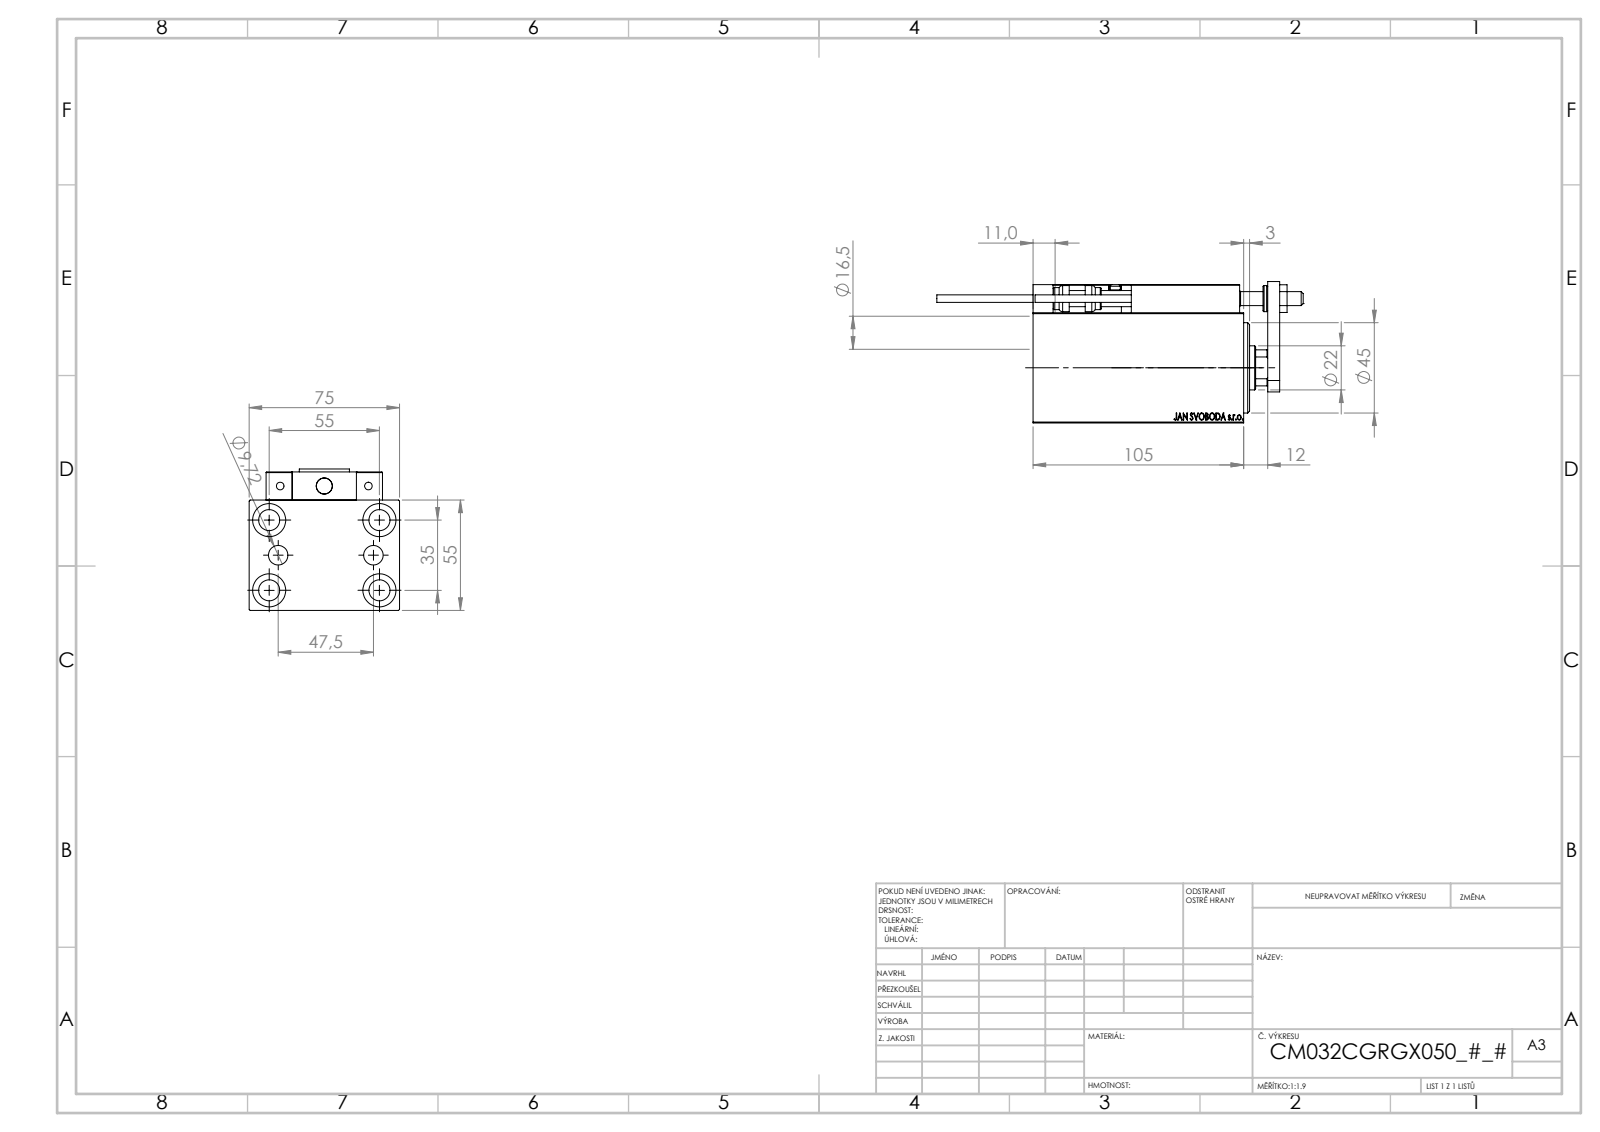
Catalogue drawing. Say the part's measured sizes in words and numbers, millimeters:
The part is named "V450CM_VC_B; MAGNET; V450CM_C_Body; V450CM_C_VCP (+7 more)". Its 3-D file was written by "SolidWorks 2019 (CONFIG_CONTROL_DESIGN)". It is 23 solids with 1278 faces: 560 planar, 184 cylindrical and 534 other. Overall it measures 182.7 by 75 by 70.5 millimeters. Its volume is 415 378 cubic millimeters and its surface area 105 587 square millimeters. Round holes: 6 of diameter 4, 5 of diameter 8, 5 of diameter 10.5, 5 of diameter 16.5, 4 of diameter 3.2, 2 of diameter 5, 2 of diameter 9.72, 1 of diameter 7, 1 of diameter 22, 1 of diameter 25.5, 1 of diameter 32, 1 of diameter 34. Round bosses or shafts: 2 of diameter 5, 2 of diameter 3.8, 1 of diameter 13, 1 of diameter 11. Partial cylindrical surfaces (rounded edges, fillets, slot ends): 30 of radius 0.3, 2 of radius 3, 1 of radius 10.5. The main face-to-face distances are 55, 75, 14, 10, 69, 5, 12, 25, 18, 3. The hole center spacings are 17.9, 32.6, 54.16, 11.37, 20, 23.75, 29.59, 29.69.
